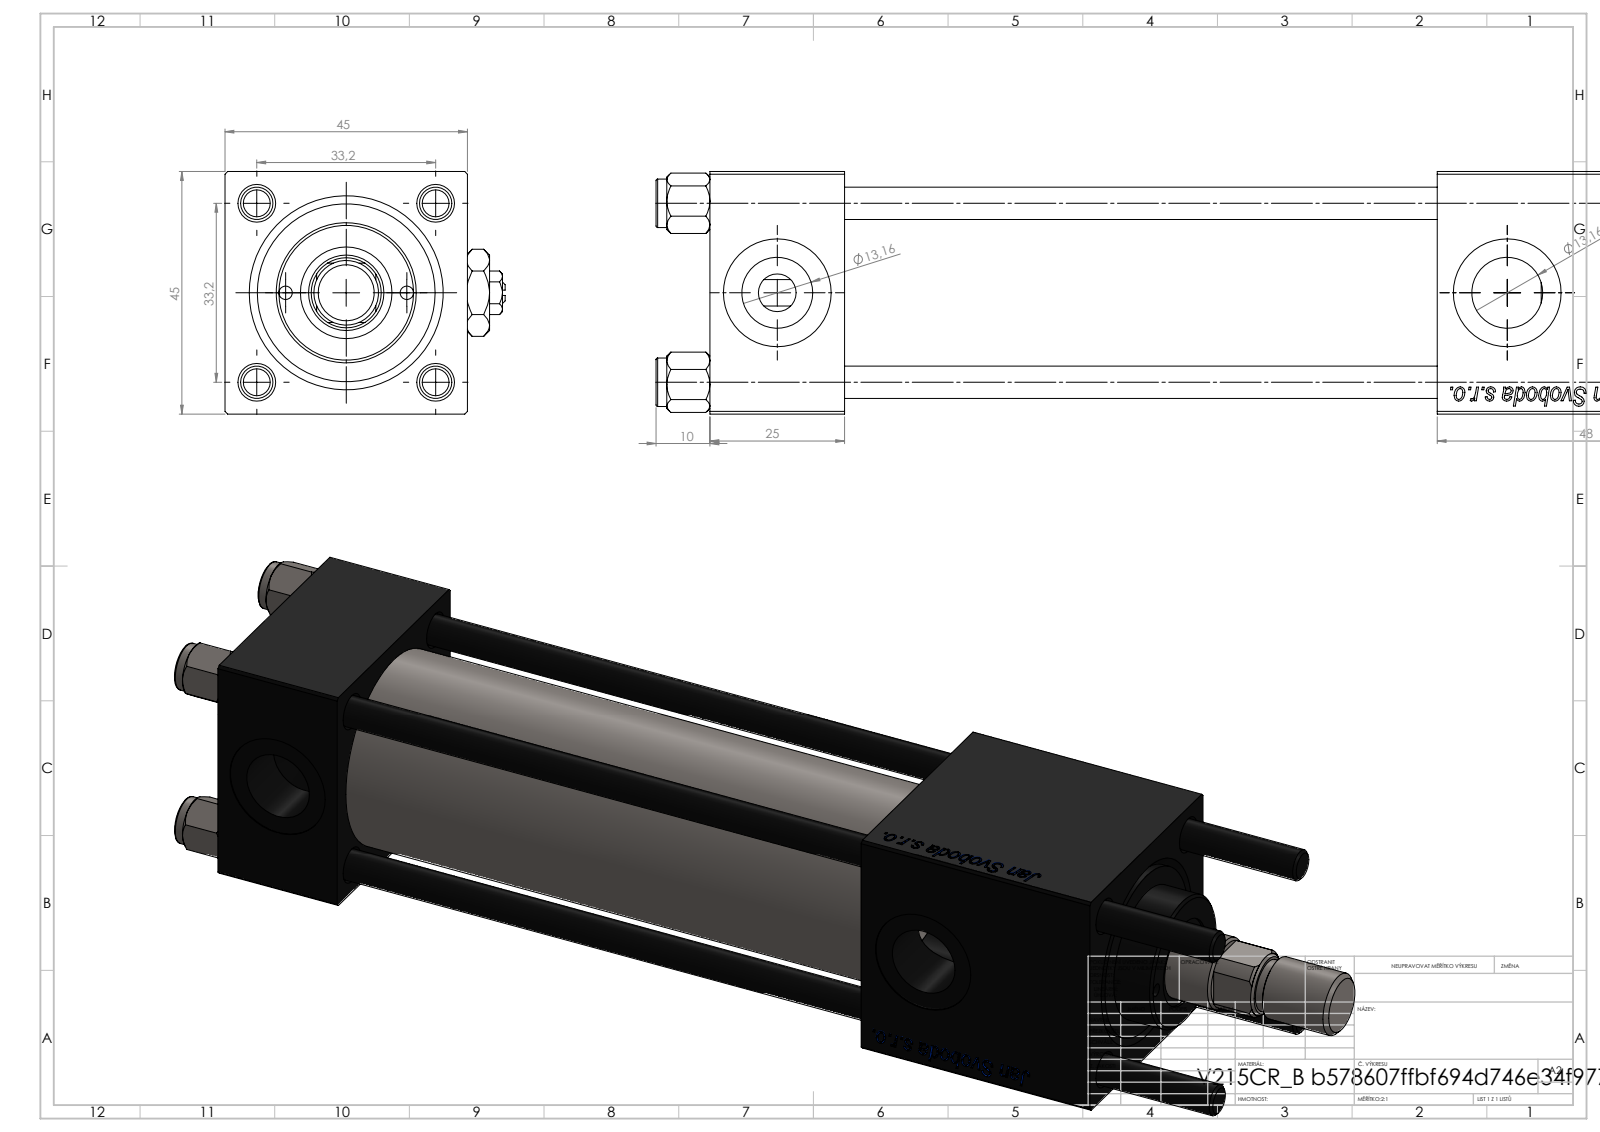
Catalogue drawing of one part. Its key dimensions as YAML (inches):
part_name: "V215CR_B_TYCINKA; V215_VC_A; V215CR_B-1; NUT_M5_B (+3 more)"
step_written_by: "SolidWorks 2019 (CONFIG_CONTROL_DESIGN)"
units: inches
bodies: {solids: 13, faces: 1228, planar: 460, cylindrical: 92, other: 676}
overall_size: [9.213, 2.047, 1.772]
volume: 14.34
surface_area: 147.3
round_holes:
  - {diameter: 0.236, count: 4}
  - {diameter: 0.098, count: 2}
  - {diameter: 0.276, count: 2}
  - {diameter: 0.518, count: 2}
  - {diameter: 0.787, count: 2}
  - {diameter: 0.256, count: 1}
  - {diameter: 0.551, count: 1}
  - {diameter: 0.669, count: 1}
  - {diameter: 0.945, count: 1}
  - {diameter: 1.26, count: 1}
  - {diameter: 1.299, count: 1}
round_bosses_or_shafts:
  - {diameter: 0.354, count: 4}
  - {diameter: 1.496, count: 1}
  - {diameter: 1.024, count: 1}
  - {diameter: 0.472, count: 1}
  - {diameter: 0.394, count: 1}
partial_cylinders:
  - {radius: 0.256, count: 1}
face_to_face_distances: [1.772, 0.984, 7.205, 6.22, 5.315, 4.331, 1.89, 6.075, 5.091, 0.76]
hole_center_spacings: [0.687, 0.924, 1.276, 1.307, 0.443, 1.848, 0.886, 5.335]
